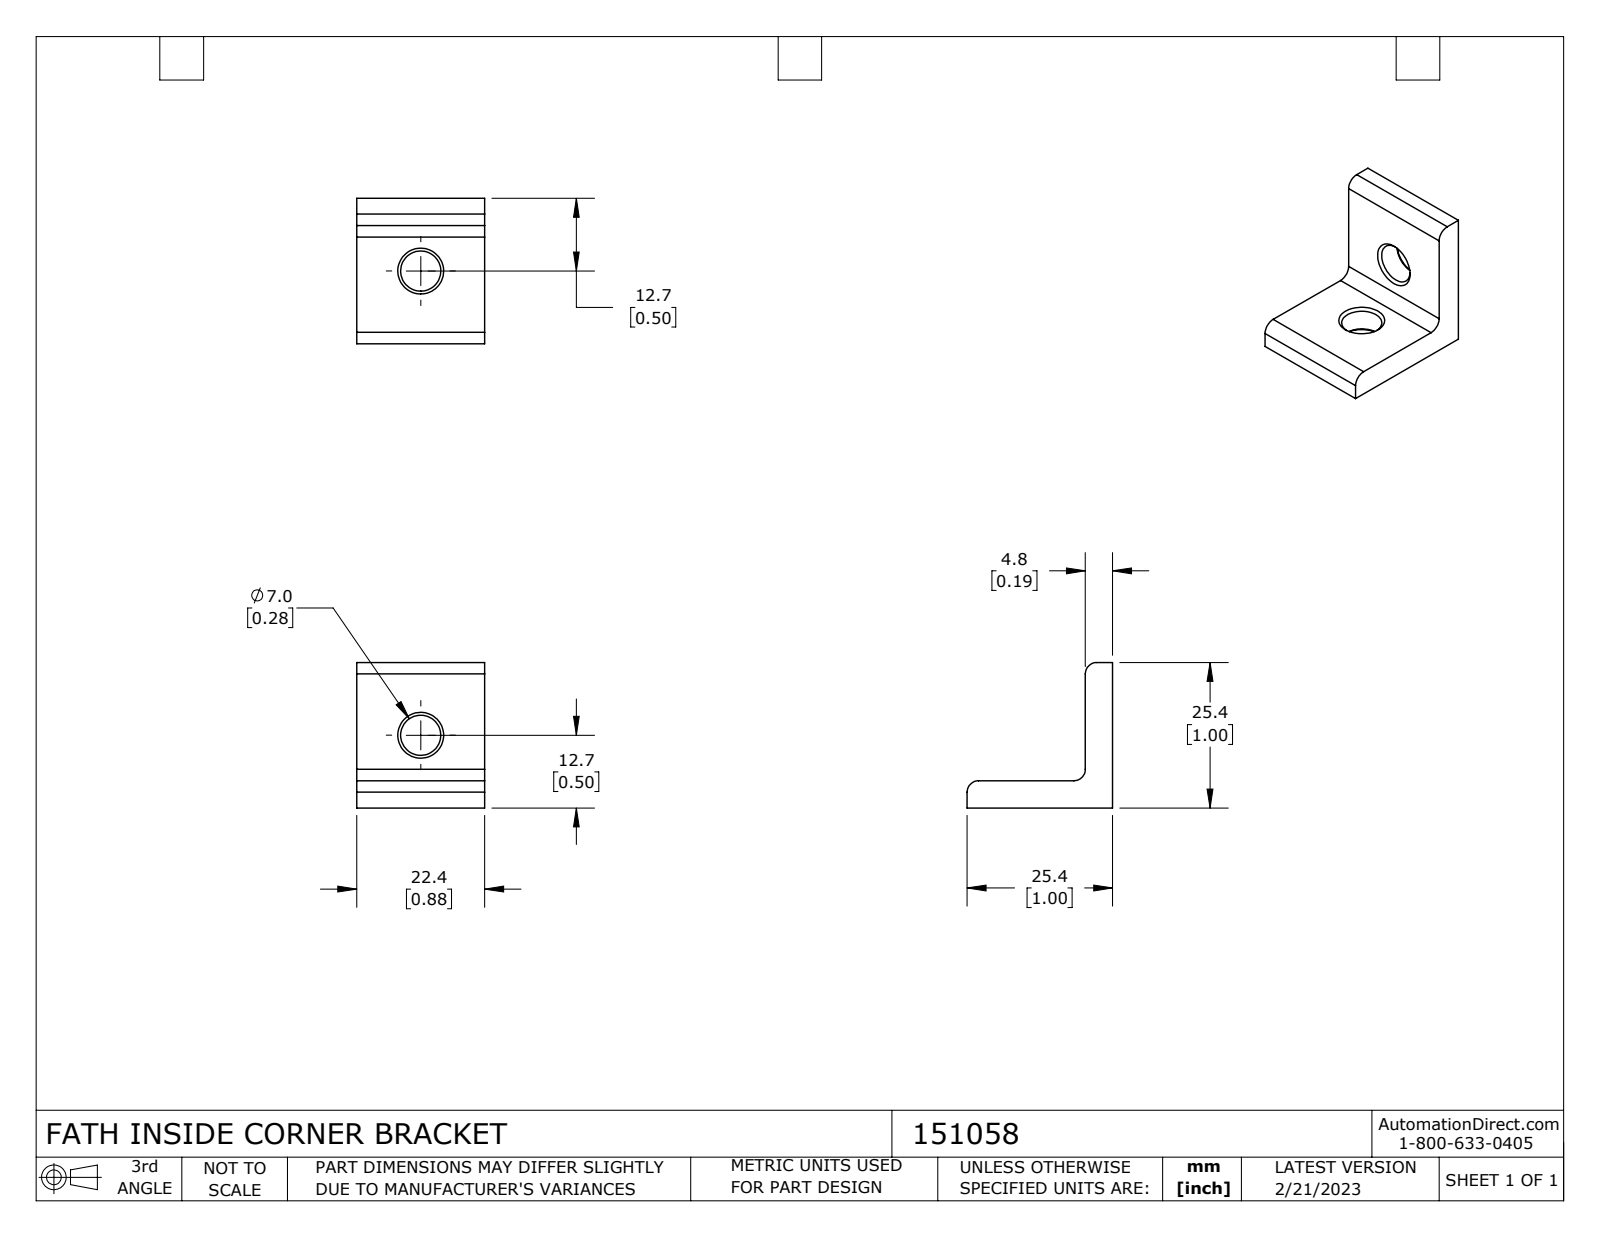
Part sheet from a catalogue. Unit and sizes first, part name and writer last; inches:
Units: inches
Overall size (bounding box): 1 × 1 × 0.88
Round holes (diameter × count): ⌀0.276 ×2
Partial cylindrical surfaces — rounded edges, fillets, slot ends (radius × count): R0.079 ×3
Main face-to-face distances: 0.187, 0.88, 1, 0.813
Volume: 0.275 in³ · Surface area: 4.156 in²
Bodies: 1 solid, 23 faces (8 planar, 7 cylindrical, 8 other)
Part name (STEP PRODUCT): 151058
STEP written by: SolidWorks 2021 (CONFIG_CONTROL_DESIGN)
